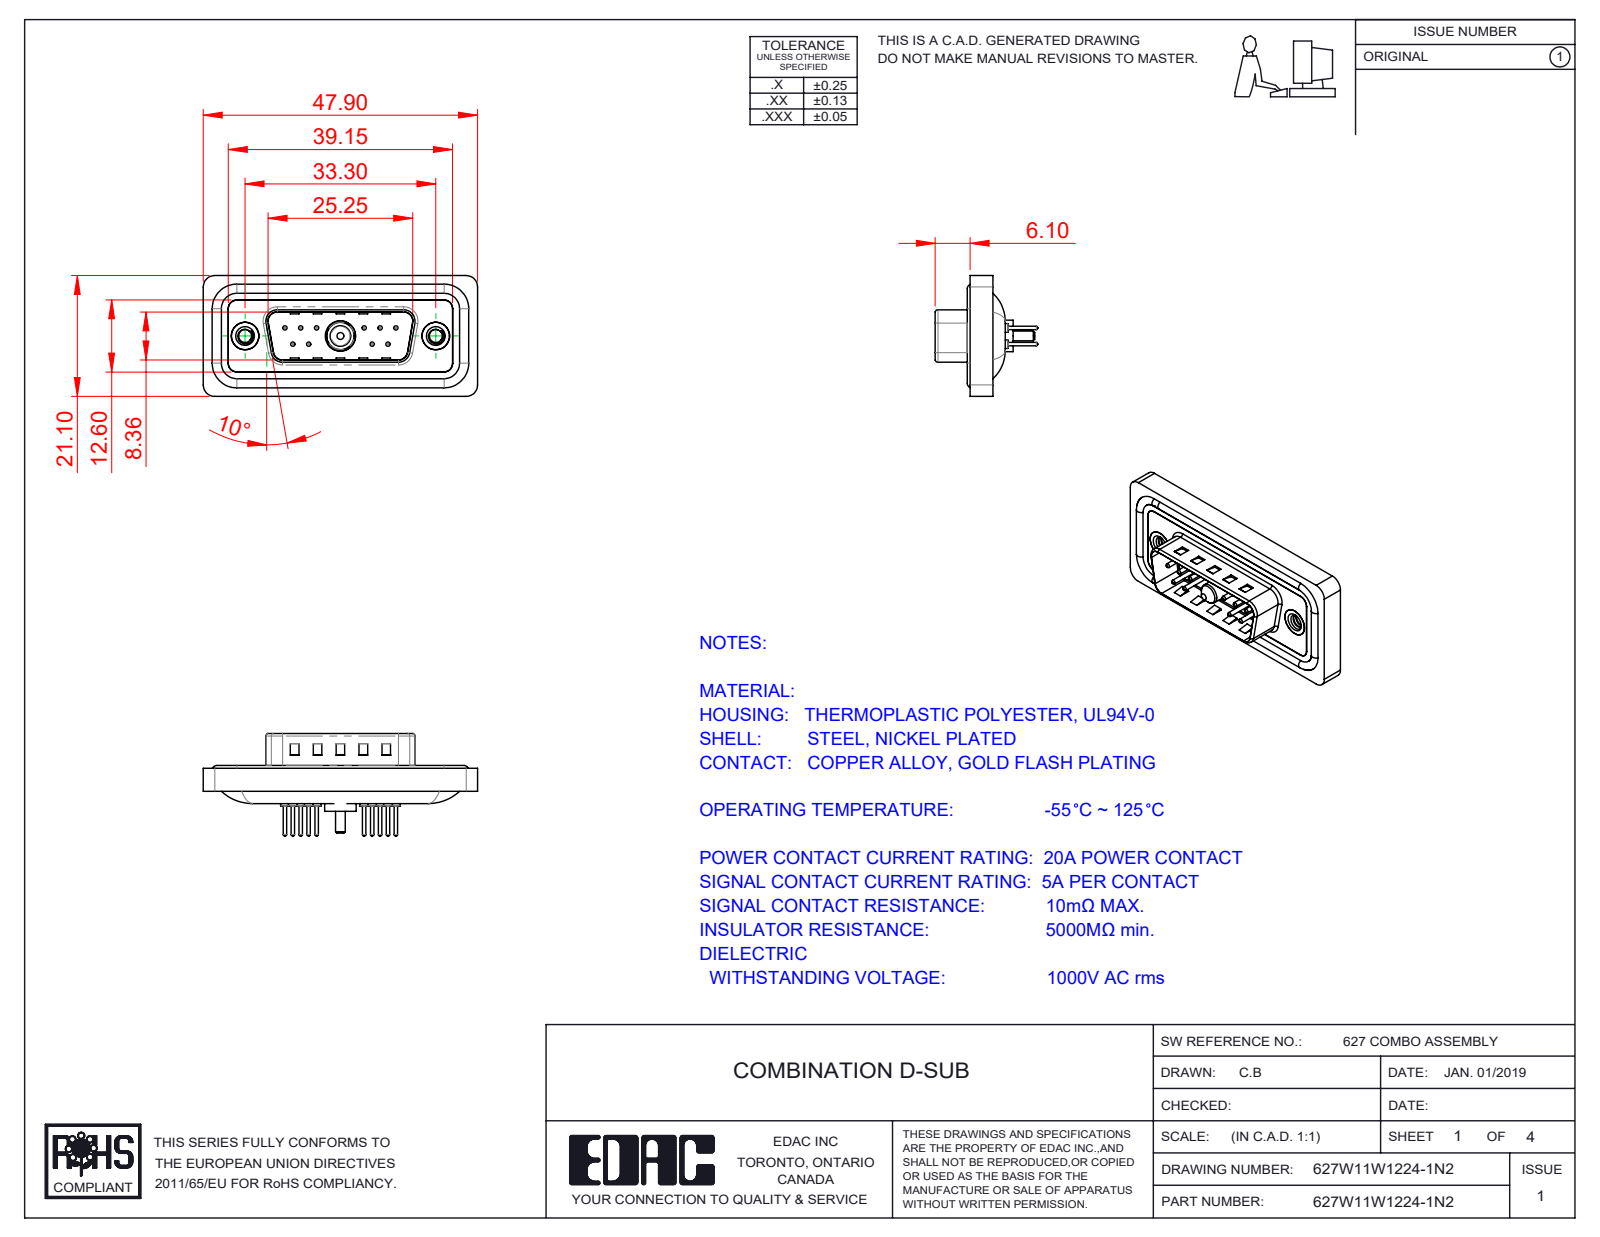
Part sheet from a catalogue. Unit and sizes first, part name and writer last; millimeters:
Units: millimetres
Overall size (bounding box): 47.9 × 21.1 × 17.9
Round holes (diameter × count): ⌀0.75 ×10, ⌀1.6 ×10, ⌀2 ×10, ⌀2.26 ×2, ⌀4 ×2, ⌀4.8 ×2, ⌀5 ×2, ⌀4.85 ×1, ⌀5.3 ×1
Round bosses / shafts (diameter × count): ⌀1.5 ×10, ⌀0.6 ×10, ⌀1.6 ×4, ⌀4.9 ×2, ⌀5.5 ×1, ⌀5.2 ×1, ⌀4.75 ×1, ⌀3.75 ×1
Partial cylindrical surfaces — rounded edges, fillets, slot ends (radius × count): R1.5 ×26, R2 ×20, R0.5 ×8, R1.6 ×8, R1 ×7, R0.25 ×4, R0.6 ×4, R0.65 ×4
Main face-to-face distances: 0.4, 1.1, 1.6, 1.5, 3.1, 0.5, 2.9, 2.5, 4.1, 0.82
Hole centre spacings: 3.16, 2.77, 13.85, 11.08, 16.62, 5.03, 5.04, 5.54
Volume: 5 433 mm³ · Surface area: 8 824 mm²
Bodies: 19 solids, 869 faces (266 planar, 347 cylindrical, 256 other)
Part name (STEP PRODUCT): 627Combo Waterproof Housing_15 Contacts; 627Combo Threaded Rivet_2; 627W11W1224-1N2; 627Combo Shell Rear_15 Contacts (+5 more)
STEP written by: SolidWorks 2020 (CONFIG_CONTROL_DESIGN)
